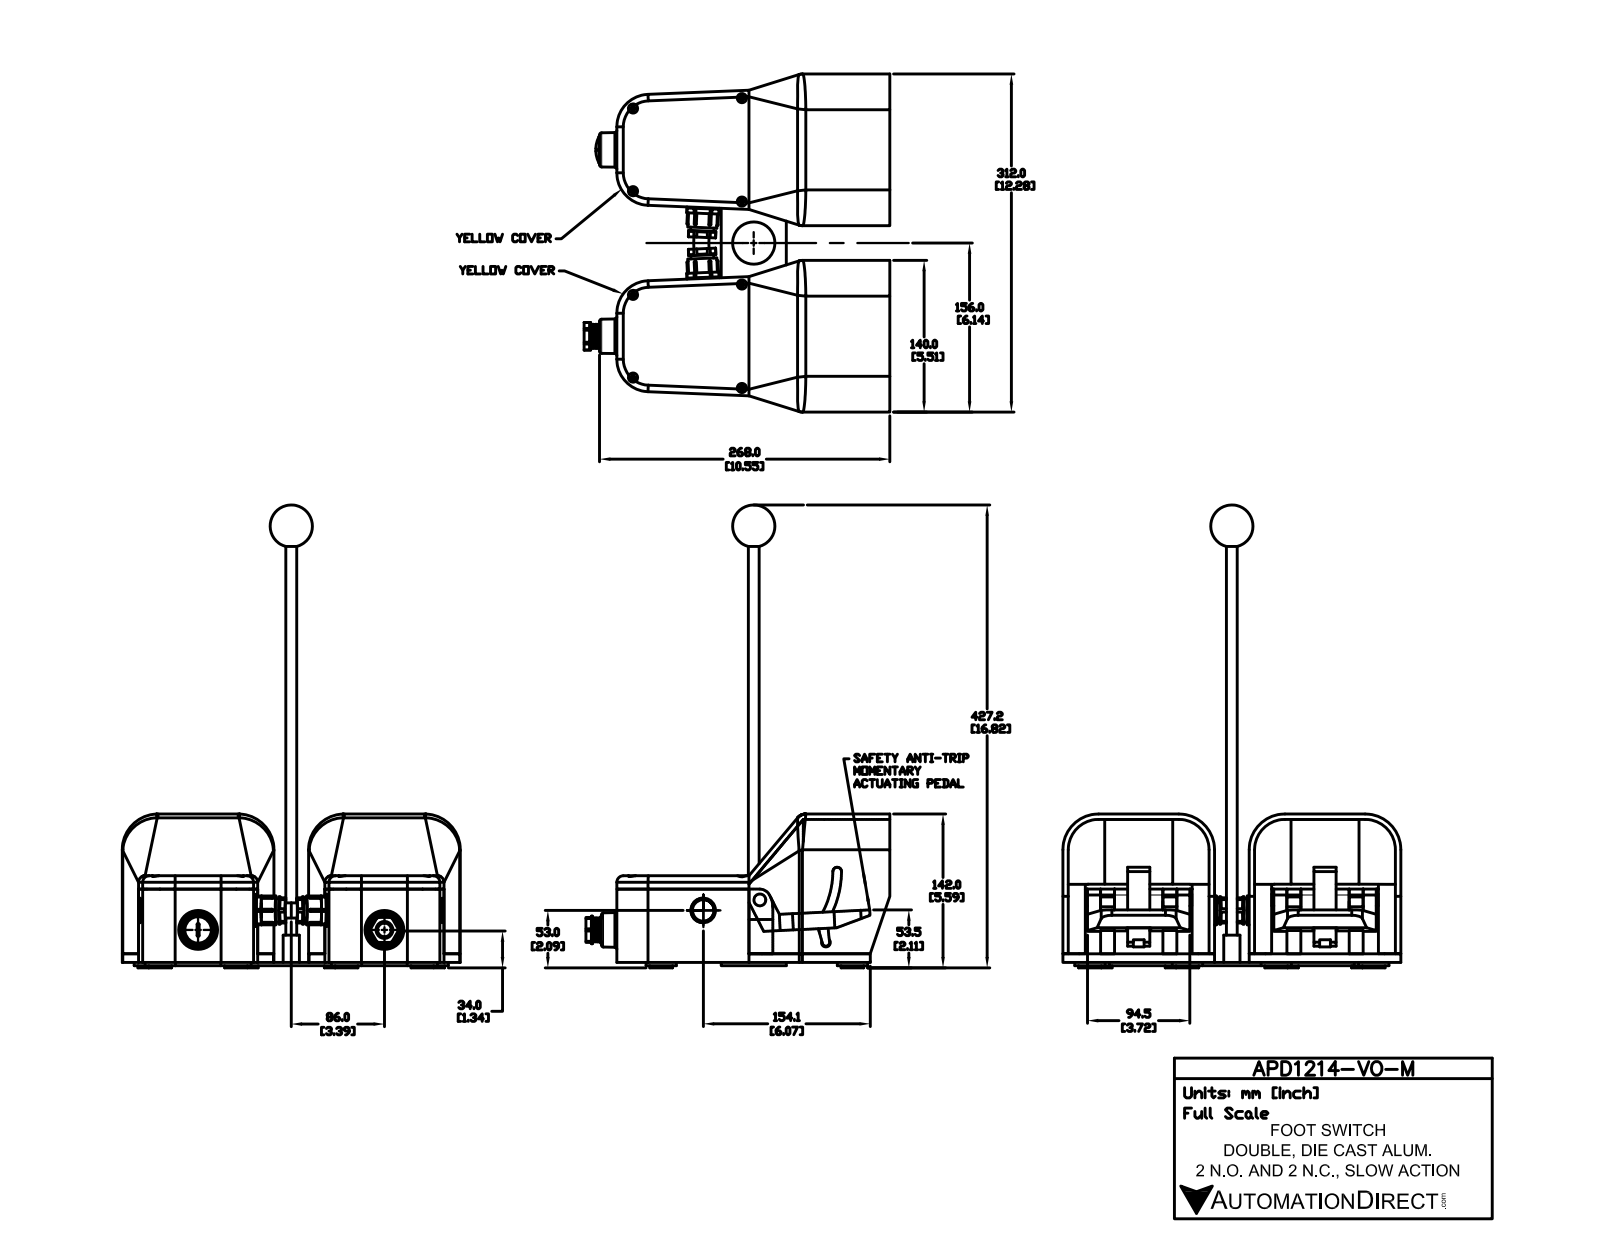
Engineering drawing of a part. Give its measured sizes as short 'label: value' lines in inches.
name: APD1214-V0-M
written by: SolidWorks 2015 (AUTOMOTIVE_DESIGN)
unit: in
bodies: 38 solids, 865 faces (514 planar, 237 cylindrical, 114 other)
size: 16.817 × 12.283 × 11.112
volume: 197.7 in³; area: 906.5 in²
holes: 8× ⌀0.335, 4× ⌀0.896, 1× ⌀0.498, 1× ⌀0.614
bosses: 8× ⌀1.102, 8× ⌀0.827, 4× ⌀0.782, 2× ⌀1.171, 2× ⌀1.051, 2× ⌀0.992, 2× ⌀0.846, 1× ⌀1.004
rounds: 34× R0.039, 12× R0.042, 11× R0.394, 5× R0.236, 4× R1.102, 4× R1.181, 4× R1.299, 2× R0.787
face distances: 0.197, 5.315, 6.772, 0.315, 2.348, 5.512, 2.664, 2.349, 2.663, 0.118
hole spacings: 3.976, 5.206, 6.772, 3.004, 3.76, 5.211, 7.52, 8.172
